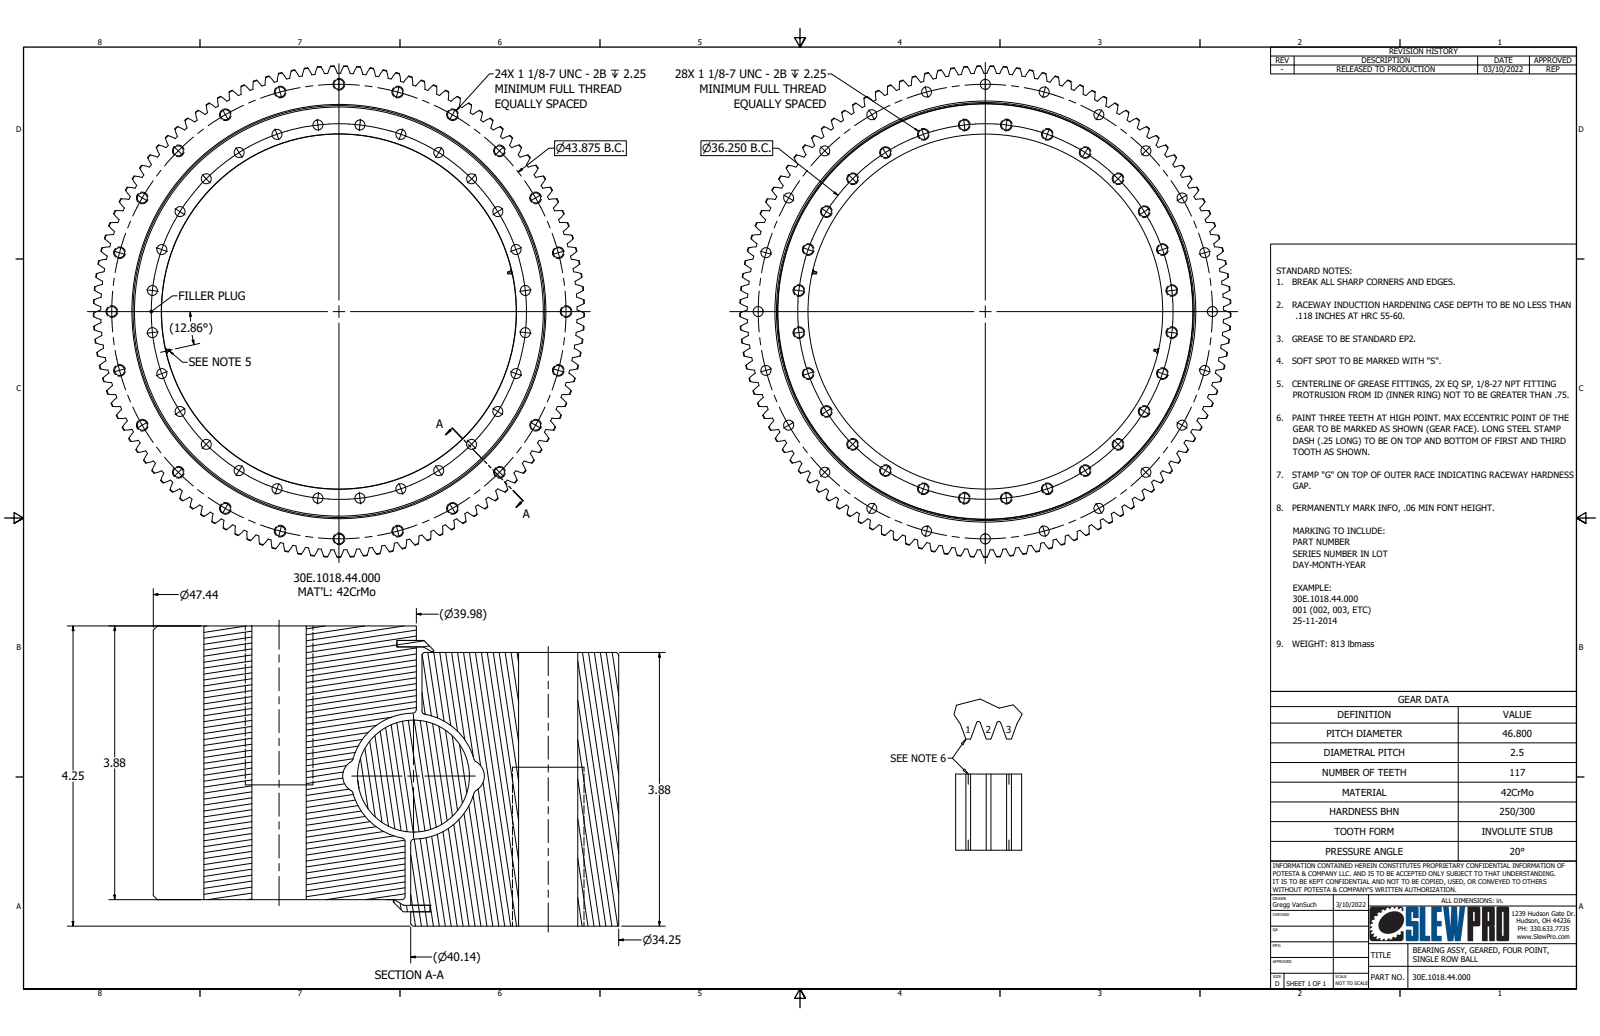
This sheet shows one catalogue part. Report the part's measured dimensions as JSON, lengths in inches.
{"part_name": "30E.1018.44.000; 1_8 NPT Fitting; Spur Gears1", "step_written_by": "Autodesk Inventor 2021 (AUTOMOTIVE_DESIGN)", "units": "inches", "bodies": {"solids": 8, "faces": 1015, "planar": 36, "cylindrical": 540, "other": 439}, "overall_size": [47.439, 47.435, 4.25], "volume_in3": 2867, "surface_area_in2": 5880, "round_holes": [[0.97, 52], [0.1, 2], [1.899, 1], [34.25, 1], [39.592, 1], [39.983, 1], [40.303, 1], [40.534, 1]], "round_bosses_or_shafts": [[40.533, 1], [40.143, 1], [39.823, 1], [39.591, 1], [1.897, 1]], "partial_cylinders_radius": [[4.164, 234], [23, 1], [23.72, 1]], "face_to_face_distances": [3.875, 0.375, 4.25, 3.5, 3.75, 0.093, 0.204, 4.046, 0.171, 3.671], "hole_center_spacings": [30.694, 34.216, 35.341, 28.341, 8.067, 11.972, 15.728, 18.125]}
